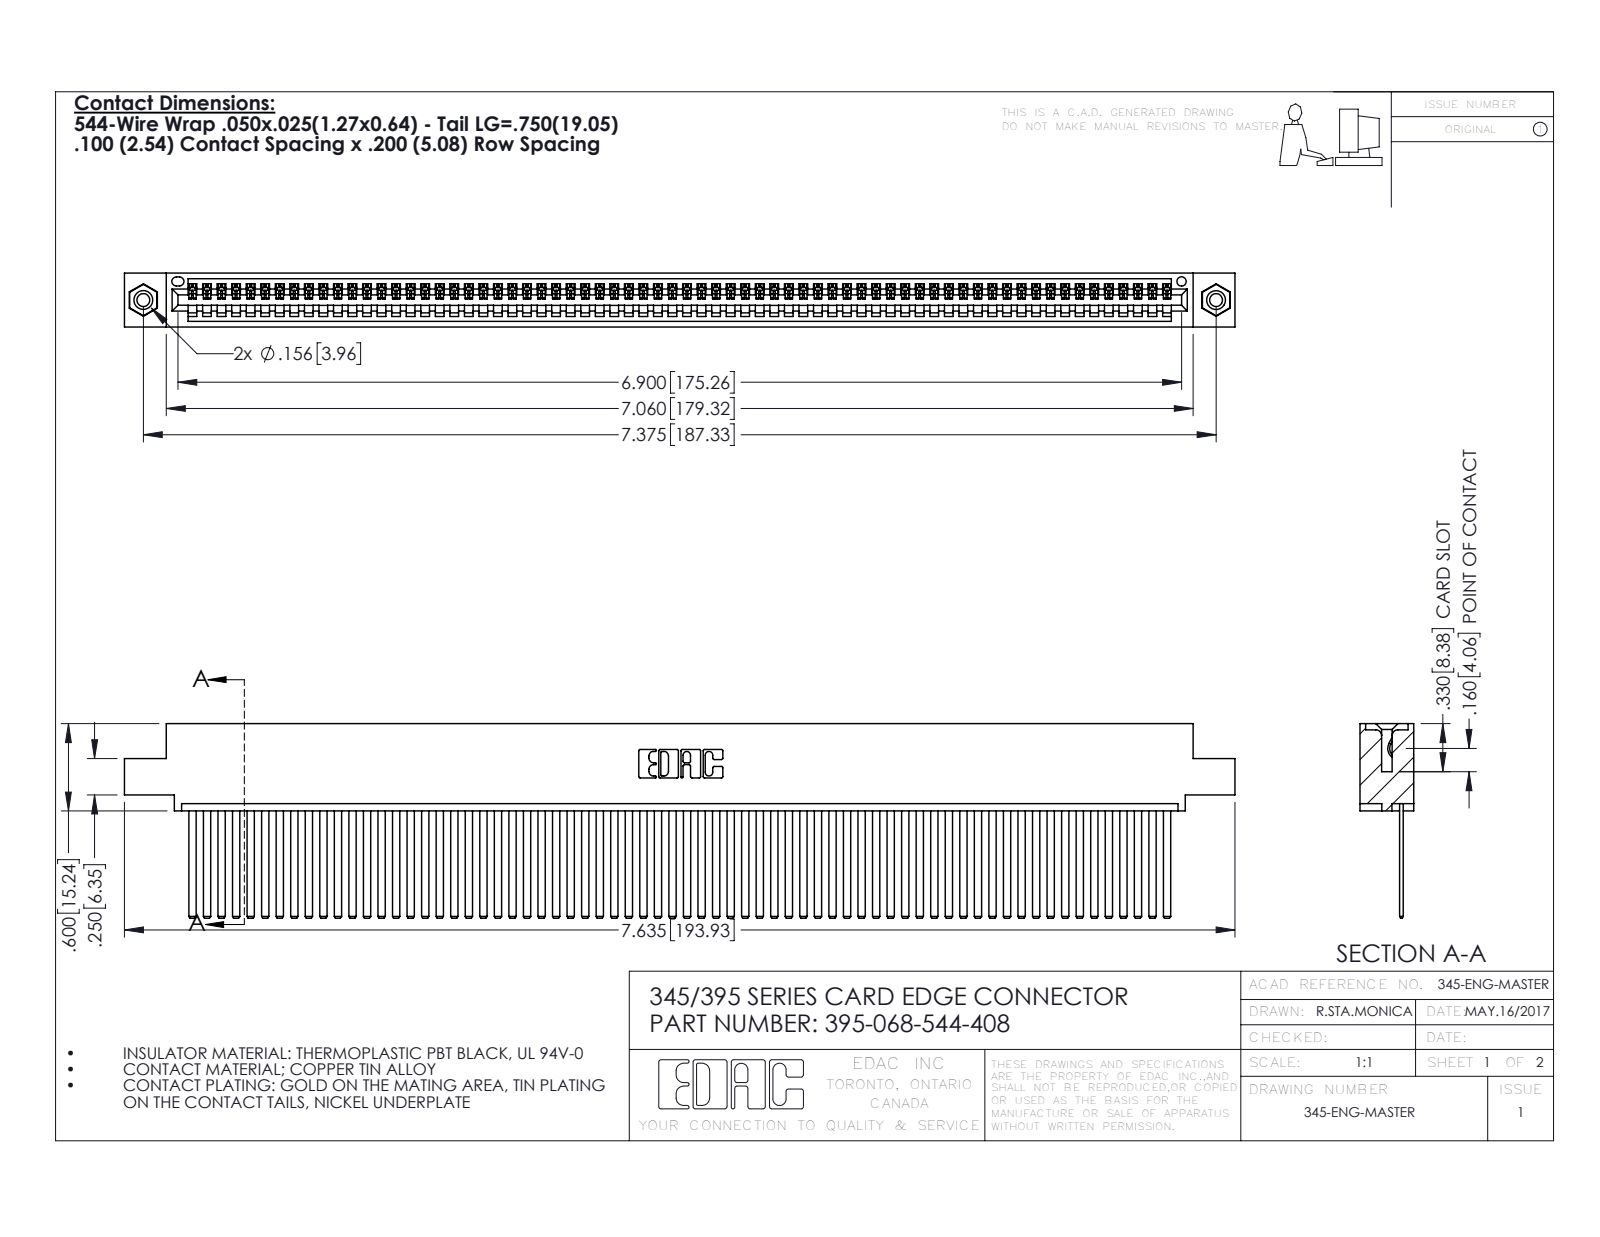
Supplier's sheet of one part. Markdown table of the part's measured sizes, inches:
| quantity | value |
| --- | --- |
| part name | 345 Part_0.110 Offset - 0.156 Dia-TI; 395-068-544-408; 345-250-001_345-250-003-102; 345-292-001_345-293-144 |
| STEP written by | SolidWorks 2016 (CONFIG_CONTROL_DESIGN) |
| units | inches |
| bodies | 71 solids, 3726 faces (2564 planar, 1146 cylindrical, 16 other) |
| overall size | 7.635 × 1.337 × 0.37 |
| volume | 1.18 in³ |
| surface area | 44.21 in² |
| round holes (diameter × count) | 0.089 × 2, 0.125 × 2, 0.156 × 2, 0.064 × 1 |
| round bosses / shafts (diameter × count) | 0.155 × 2 |
| partial cylindrical surfaces (radius × count) | 0.006 × 136, 0.01 × 22, 0.007 × 6, 0.031 × 6, 0.026 × 3, 0.031 × 2, 0.04 × 2, 0.014 × 1 |
| main face-to-face distances | 0.072, 0.298, 0.025, 0.098, 0.272, 0.37, 0.2, 0.225, 0.149, 0.072 |
| hole center spacings | 0.27, 7.139, 7.375 |
